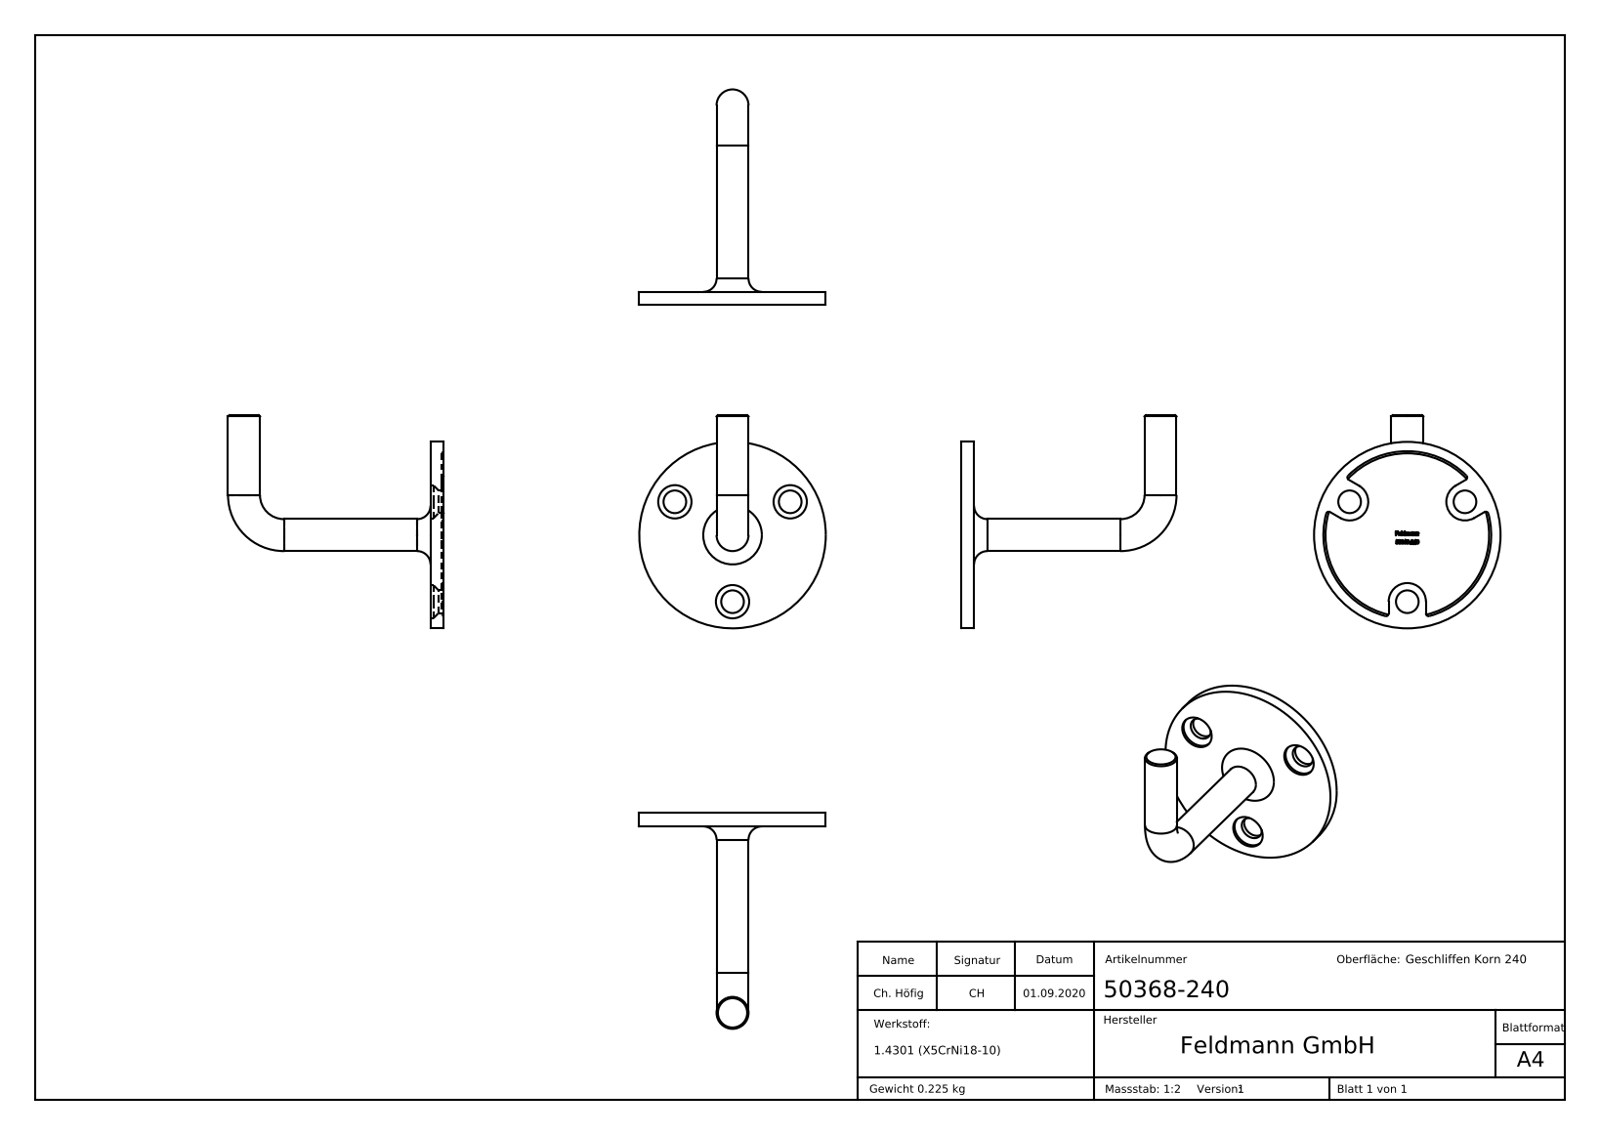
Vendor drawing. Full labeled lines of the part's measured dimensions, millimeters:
Part name (STEP PRODUCT): 50368-240
STEP written by: SolidWorks 2018 (CONFIG_CONTROL_DESIGN)
Units: millimetres
Bodies: 1 solid, 290 faces (125 planar, 29 cylindrical, 136 other)
Overall size (bounding box): 81 × 80 × 70
Volume: 28 461 mm³ · Surface area: 12 968 mm²
Round holes (diameter × count): ⌀8.5 ×3, ⌀12.5 ×3
Round bosses / shafts (diameter × count): ⌀12 ×2, ⌀70 ×1
Partial cylindrical surfaces — rounded edges, fillets, slot ends (radius × count): R1 ×6, R7 ×3
Main face-to-face distances: 4.2, 0.8, 5, 14, 0.9, 4.1, 2.97, 0.39, 4.09, 3.66
Hole centre spacings: 43.3
